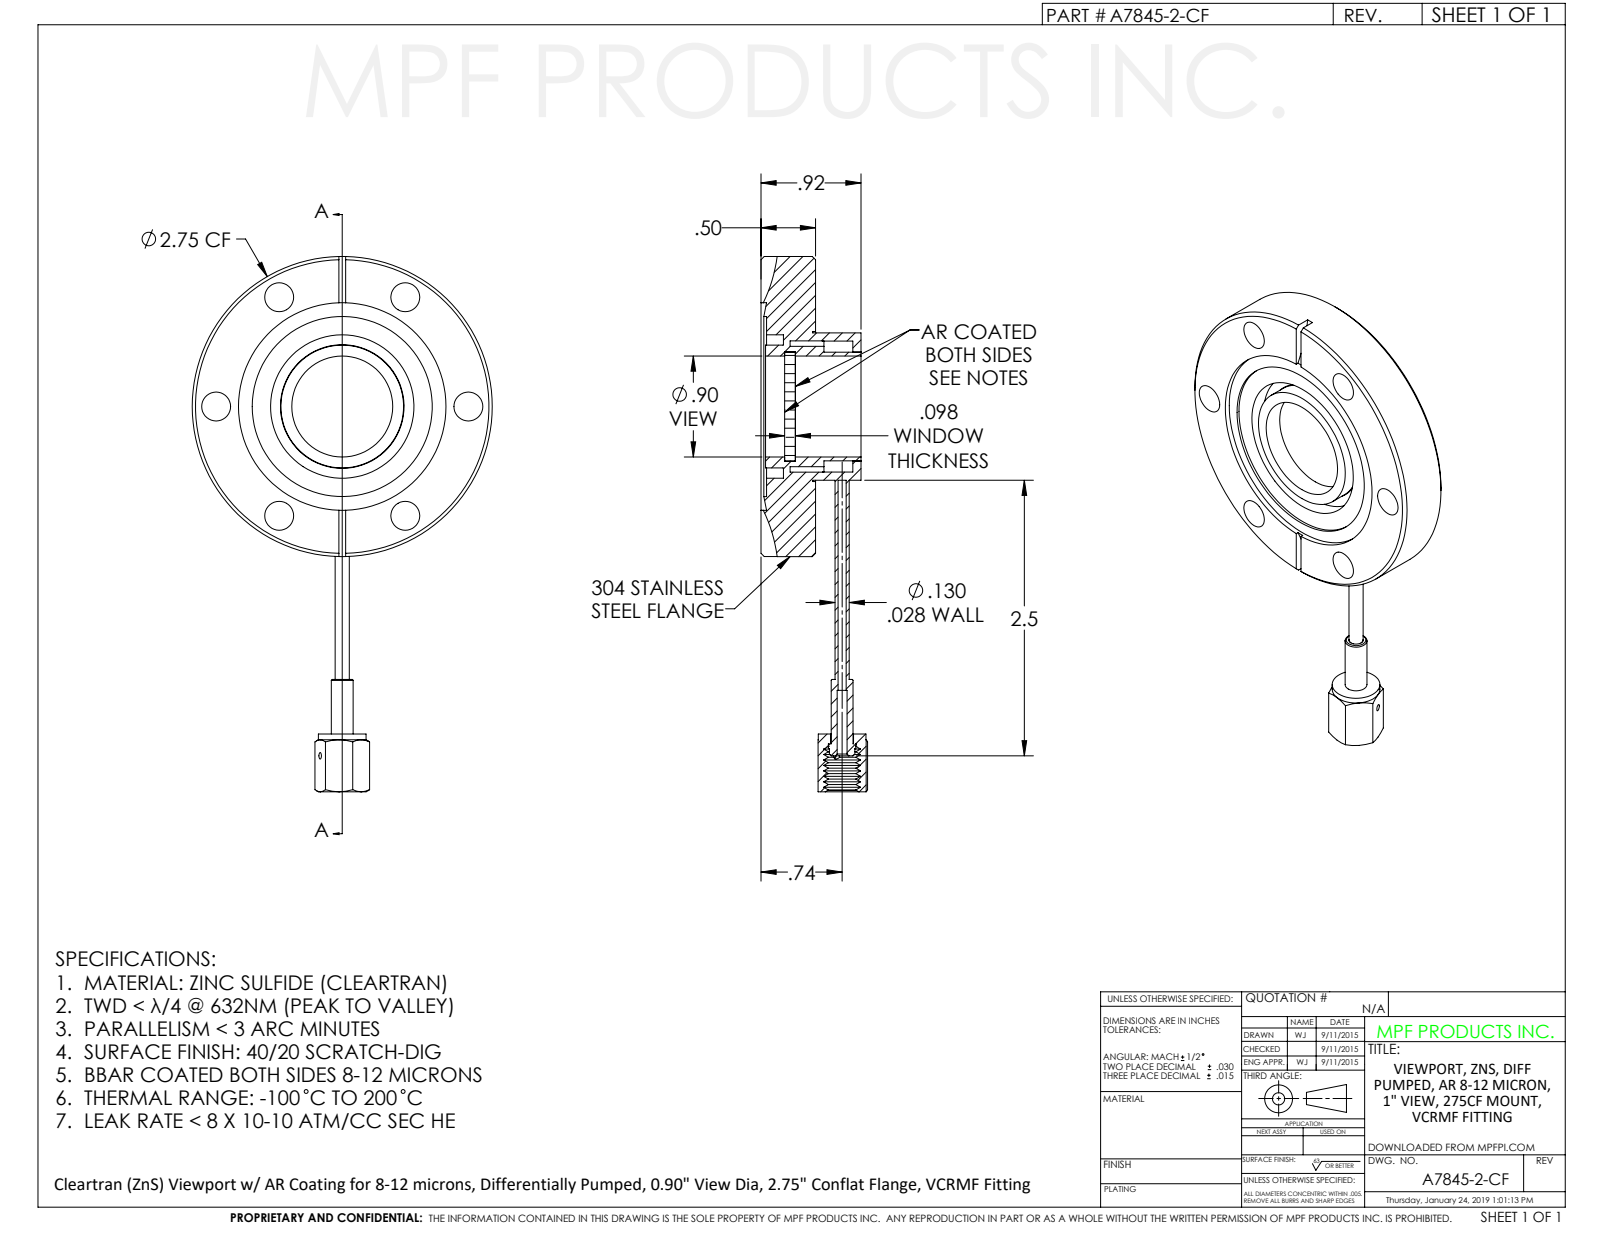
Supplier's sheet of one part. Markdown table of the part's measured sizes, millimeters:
| quantity | value |
| --- | --- |
| part name | A7845-2-CF |
| STEP written by | SolidWorks 2012 (CONFIG_CONTROL_DESIGN) |
| units | millimeters |
| bodies | 1 solid, 220 faces (52 planar, 95 cylindrical, 73 other) |
| overall size | 124.6 × 69.9 × 25.5 |
| volume | 42 840 mm³ |
| surface area | 25 490 mm² |
| round holes (diameter × count) | 6.7 × 6, 1.3 × 4, 1.5 × 1, 1.8 × 1, 2.3 × 1, 2.8 × 1, 5.3 × 1, 6.4 × 1, 23.5 × 1, 25.4 × 1, 30.5 × 1, 31.5 × 1 |
| round bosses / shafts (diameter × count) | 69.9 × 1, 38.1 × 1, 36.2 × 1, 34.8 × 1, 34.3 × 1, 32.8 × 1, 28.6 × 1, 26.4 × 1 |
| partial cylindrical surfaces (radius × count) | 34.9 × 2 |
| main face-to-face distances | 12.7, 7, 8.6, 0.4, 4.1, 4.4, 1.9, 5.7, 15.3, 18.2 |
| hole center spacings | 29.4, 14.6, 18.2, 20.7, 25.4, 32.8, 38.8, 42.7 |
